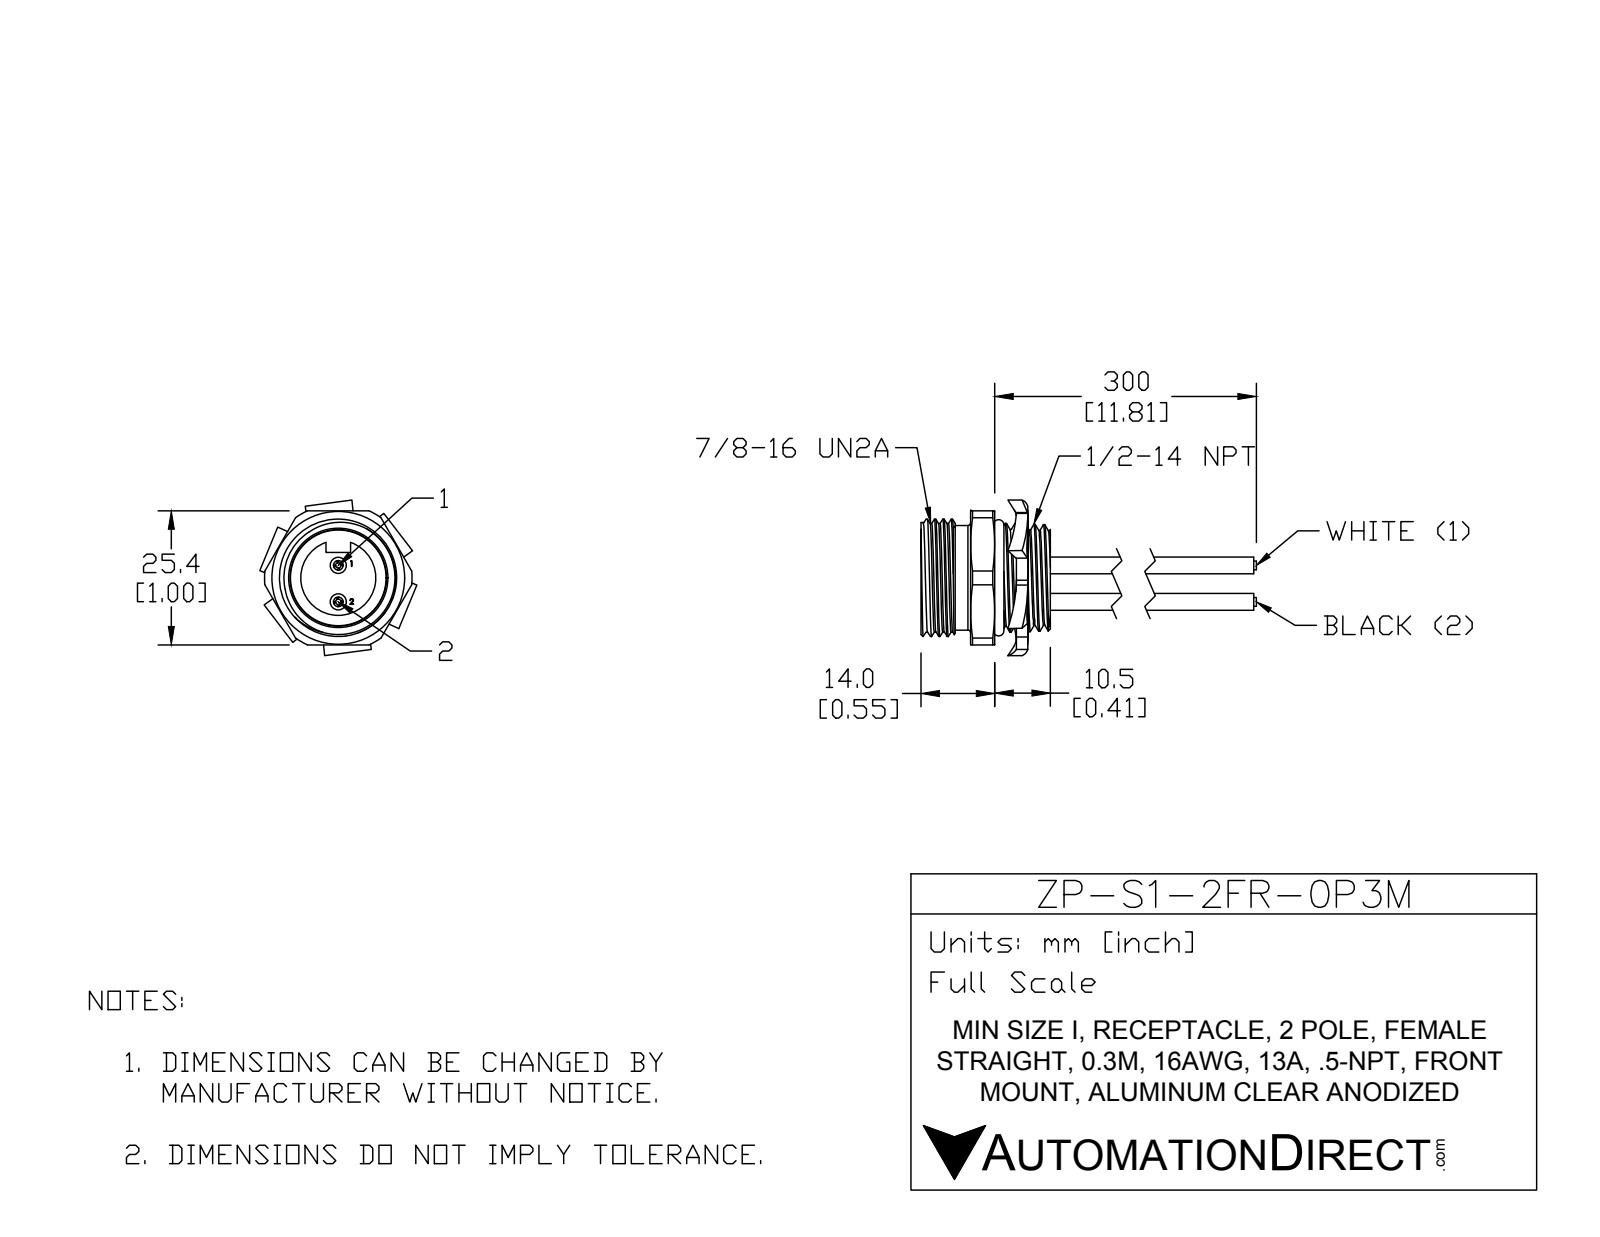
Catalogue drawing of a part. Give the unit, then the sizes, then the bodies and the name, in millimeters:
Units: millimetres
Overall size (bounding box): 49.51 × 29.77 × 29.48
Round holes (diameter × count): ⌀3.05 ×2, ⌀18.29 ×1, ⌀19.61 ×1
Round bosses / shafts (diameter × count): ⌀3.18 ×2, ⌀25.37 ×1, ⌀22.22 ×1, ⌀20.6 ×1, ⌀19.81 ×1, ⌀18.19 ×1, ⌀18.14 ×1, ⌀14.22 ×1
Partial cylindrical surfaces — rounded edges, fillets, slot ends (radius × count): R13.97 ×1
Main face-to-face distances: 15.11, 25.4, 4.57, 10.54, 7.8, 12.37, 22.91, 7.01, 0.79, 5.36
Hole centre spacings: 2.36, 4.55, 6.91
Volume: 8 759 mm³ · Surface area: 5 699 mm²
Bodies: 1 solid, 176 faces (62 planar, 56 cylindrical, 58 other)
Part name (STEP PRODUCT): MIN-2FR-ZZ
STEP written by: SolidWorks 2015 (AUTOMOTIVE_DESIGN)
